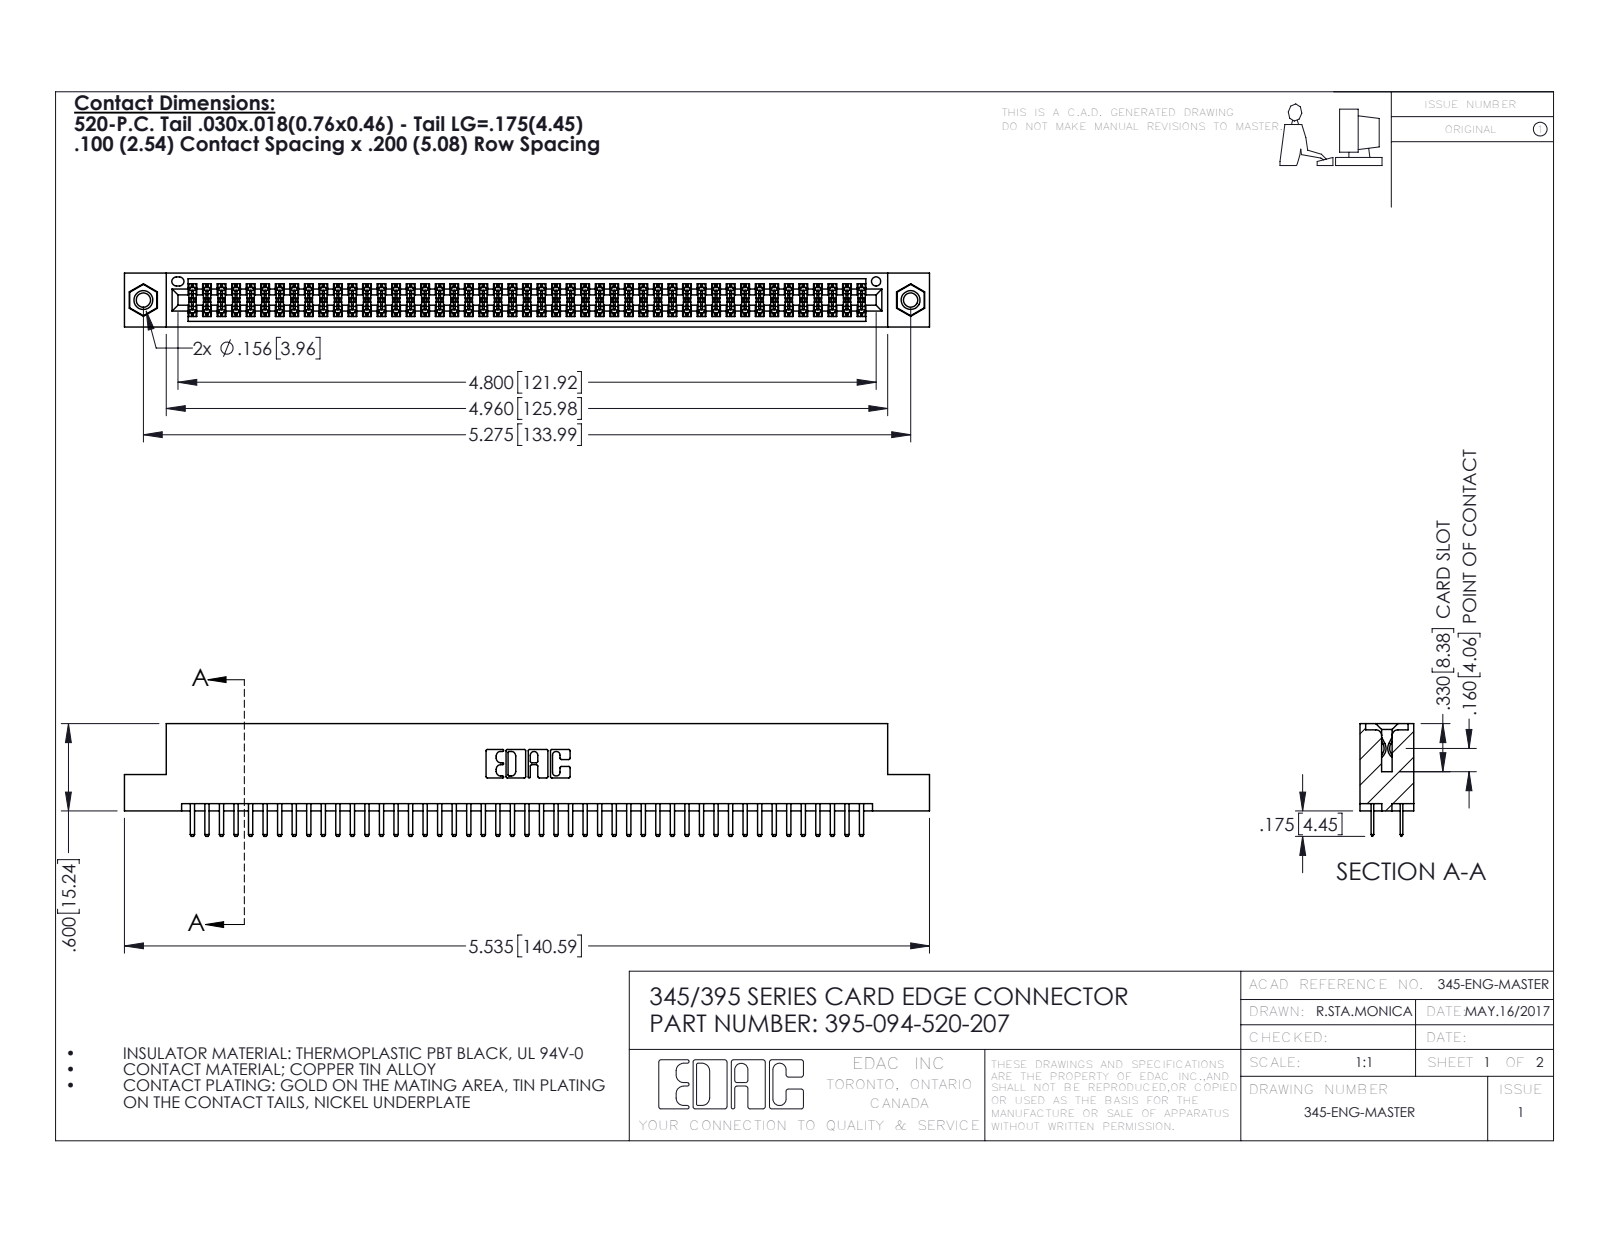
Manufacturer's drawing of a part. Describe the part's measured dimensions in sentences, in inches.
The part is named "395-094-520-207; 345-292-001_345-293-120; 345-250-001_345-250-005-103; 345 Part_Flush Mounting Lugs - 0.156 Dia-TI". Its 3-D file was written by "SolidWorks 2016 (CONFIG_CONTROL_DESIGN)". It is 97 solids with 5262 faces: 3402 planar, 1844 cylindrical and 16 other. Overall it measures 5.535 by 0.775 by 0.37 inches. Its volume is 0.833 cubic inches and its surface area 31.33 square inches. Round holes: 2 of diameter 0.098, 2 of diameter 0.125, 2 of diameter 0.156, 1 of diameter 0.064. Round bosses or shafts: 2 of diameter 0.155. Partial cylindrical surfaces (rounded edges, fillets, slot ends): 141 of radius 0.006, 98 of radius 0.01, 22 of radius 0.01, 6 of radius 0.007, 6 of radius 0.031, 3 of radius 0.026, 2 of radius 0.014, 2 of radius 0.019. The main face-to-face distances are 0.072, 0.298, 0.2, 0.37, 0.098, 0.272, 0.025, 0.225, 0.022, 0.072. The hole center spacings are 0.27, 5.039, 5.275.
